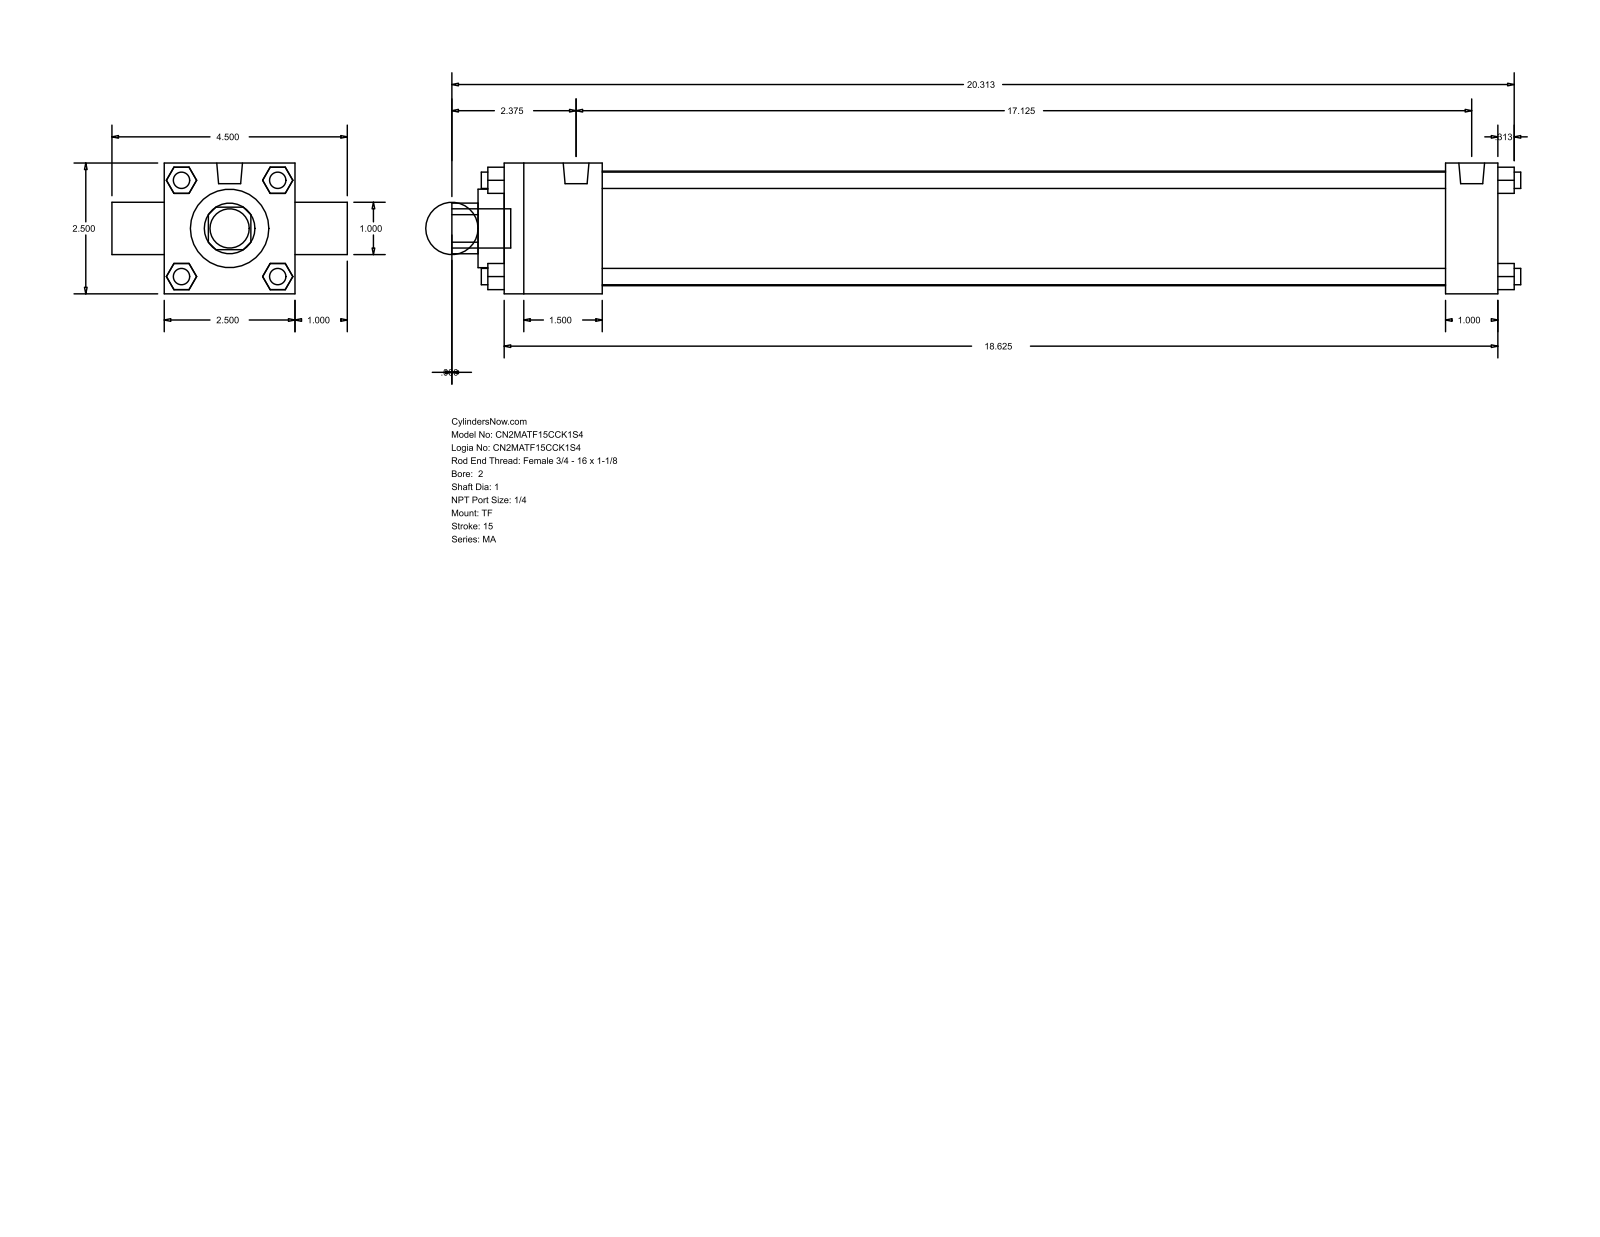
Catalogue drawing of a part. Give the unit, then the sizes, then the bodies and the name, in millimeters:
Units: millimetres
Overall size (bounding box): 519.11 × 114.3 × 63.5
Round holes (diameter × count): ⌀25.4 ×2, ⌀38.1 ×1, ⌀55.63 ×1
Round bosses / shafts (diameter × count): ⌀7.94 ×7, ⌀12.49 ×2, ⌀19.05 ×1
Partial cylindrical surfaces — rounded edges, fillets, slot ends (radius × count): R12.29 ×1
Main face-to-face distances: 63.5, 25.4, 482.6, 12.7, 47.63, 457.2, 409.57, 434.97, 88.9, 40.47
Bodies: 0 solids, 120 faces (92 planar, 28 cylindrical, 0 other)
Part name (STEP PRODUCT): MA_TF__0200_1
STEP written by: GSSL Pune (CONFIG_CONTROL_DESIGN)
